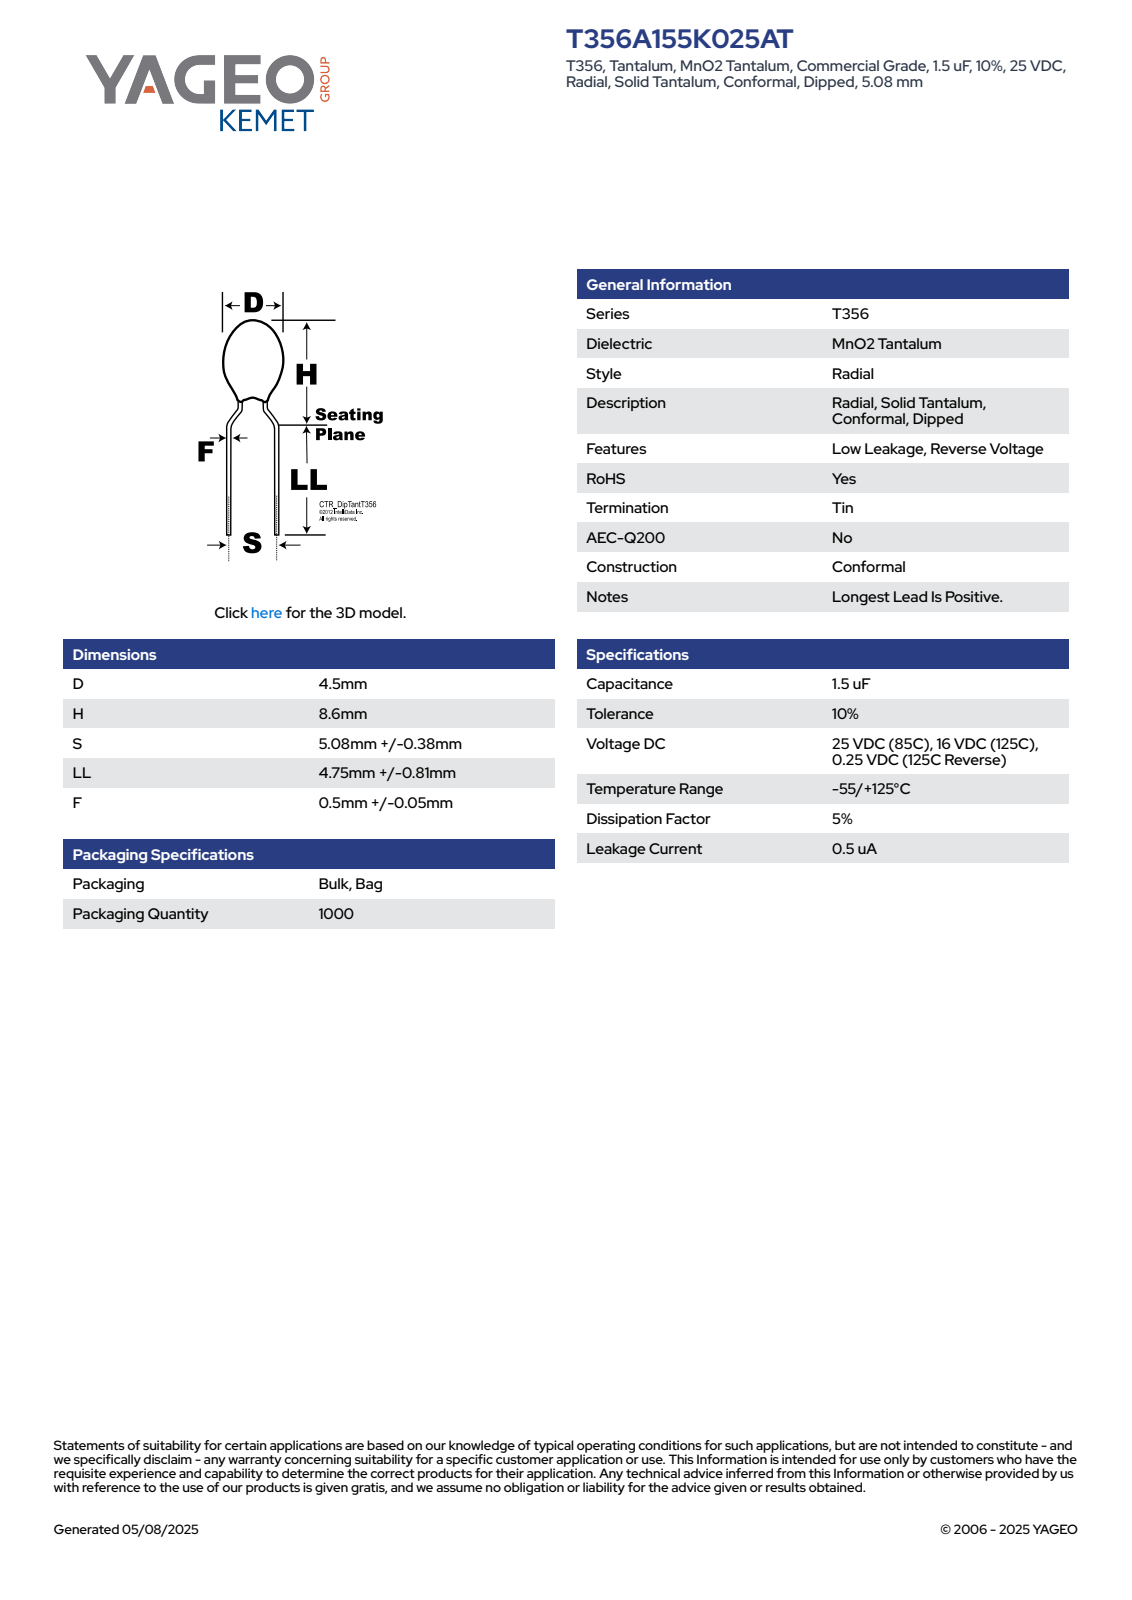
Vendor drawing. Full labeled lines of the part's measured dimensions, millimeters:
Part name (STEP PRODUCT): CTR_T356_D4.5H8.6S5.08LL5.56F0.55
STEP written by: SolidWorks 2014 (AUTOMOTIVE_DESIGN)
Units: millimetres
Bodies: 1 solid, 100 faces (27 planar, 18 cylindrical, 55 other)
Overall size (bounding box): 14.16 × 5.63 × 4.5
Volume: 91 mm³ · Surface area: 133 mm²
Round bosses / shafts (diameter × count): ⌀0.55 ×6, ⌀4.5 ×1
Partial cylindrical surfaces — rounded edges, fillets, slot ends (radius × count): R2.24 ×1
Main face-to-face distances: 6, 8.16, 14.16, 12.14, 3.98, 2.02, 11.33, 3.17, 0.81, 2.83
